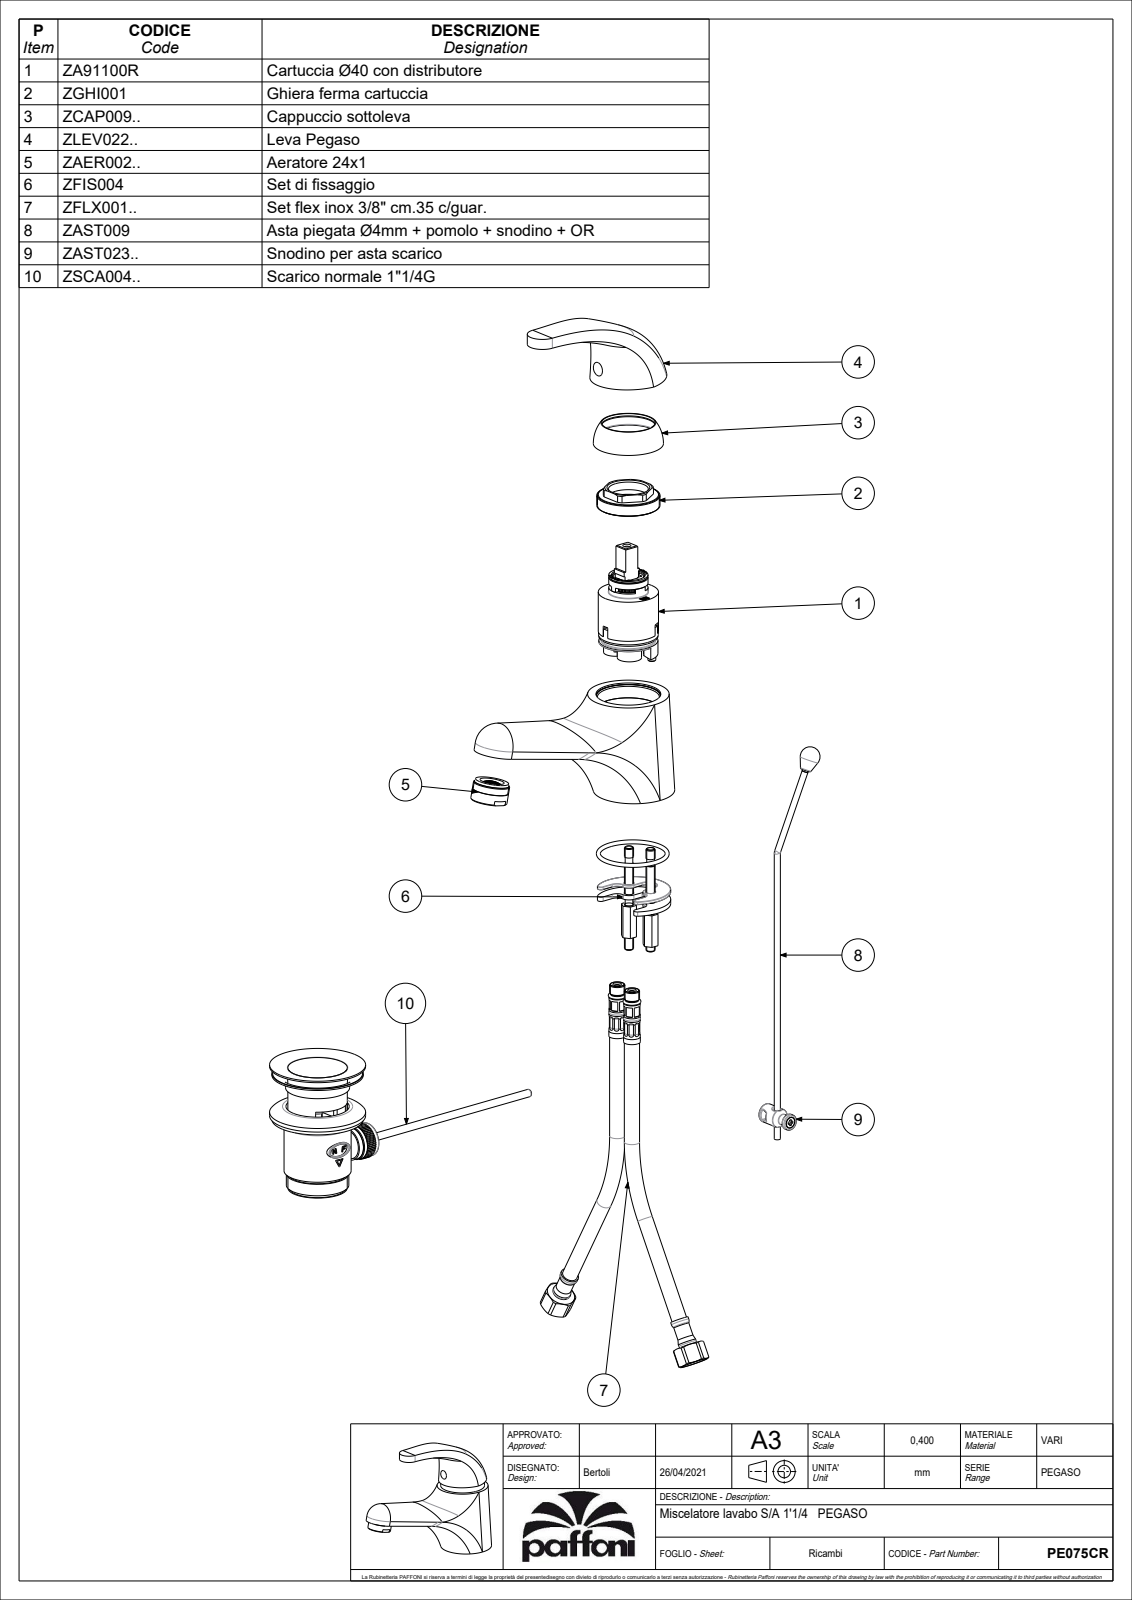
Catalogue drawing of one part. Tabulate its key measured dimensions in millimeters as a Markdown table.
| quantity | value |
| --- | --- |
| part name | PE075CR_SW0001 |
| STEP written by | CREO PARAMETRIC BY PTC INC, 2022124 (CONFIG_CONTROL_DESIGN) |
| units | millimeters |
| bodies | 4 solids, 2126 faces (1711 planar, 213 cylindrical, 202 other) |
| overall size | 176.63 × 122.07 × 53.5 |
| volume | 143 453 mm³ |
| surface area | 83 274 mm² |
| round holes (diameter × count) | 8 × 4, 5.5 × 3, 11 × 3, 7 × 2, 9 × 2, 12 × 2, 4 × 1, 6 × 1, 15 × 1, 16 × 1, 17 × 1, 20 × 1 |
| round bosses / shafts (diameter × count) | 15.9 × 2, 10 × 2, 9.4 × 2, 42 × 1, 39.2 × 1, 38.8 × 1, 34.8 × 1, 24 × 1 |
| partial cylindrical surfaces (radius × count) | 0.5 × 44, 1 × 8, 1.5 × 6, 0.3 × 4, 7.5 × 4, 2 × 2, 5.5 × 2, 6.5 × 2 |
| main face-to-face distances | 3.5, 4, 3, 1.5, 6, 15.5, 22, 6.5, 0.5, 12 |
| hole center spacings | 1.12, 9.9, 13.04, 14.53, 2, 8.6, 9.6, 10.97 |
